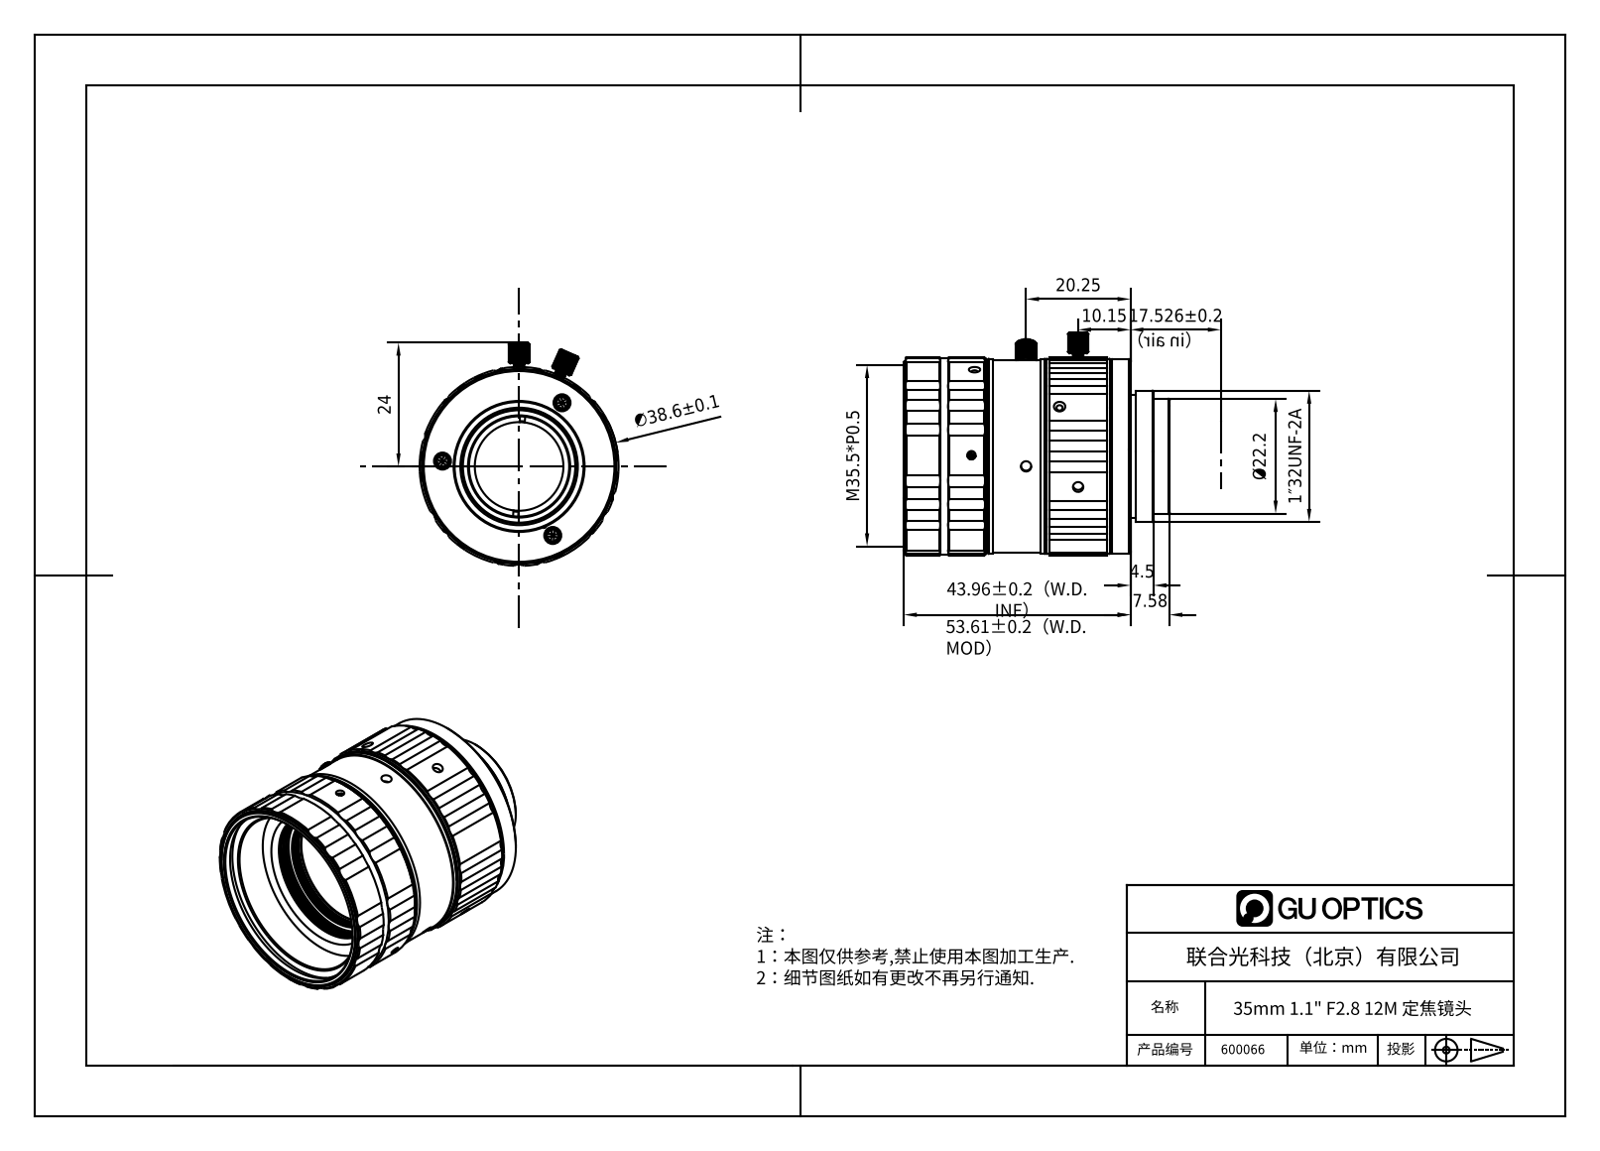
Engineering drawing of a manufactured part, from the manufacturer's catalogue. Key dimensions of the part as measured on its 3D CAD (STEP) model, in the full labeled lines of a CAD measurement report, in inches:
Part name (STEP PRODUCT): 600066
STEP written by: SolidWorks 2020 (CONFIG_CONTROL_DESIGN)
Units: inches
Bodies: 0 solids, 1146 faces (288 planar, 539 cylindrical, 319 other)
Overall size (bounding box): 2.029 × 1.707 × 1.52
Round holes (diameter × count): ⌀0.079 ×5, ⌀0.071 ×3, ⌀0.114 ×3, ⌀0.677 ×1, ⌀0.765 ×1, ⌀0.795 ×1, ⌀0.874 ×1, ⌀0.913 ×1, ⌀0.981 ×1, ⌀1.012 ×1, ⌀1.082 ×1, ⌀1.11 ×1
Round bosses / shafts (diameter × count): ⌀0.063 ×9, ⌀0.098 ×3, ⌀0.049 ×3, ⌀0.047 ×3, ⌀0.079 ×2, ⌀1.52 ×1, ⌀1.496 ×1, ⌀1.488 ×1
Partial cylindrical surfaces — rounded edges, fillets, slot ends (radius × count): R0.079 ×26, R0.118 ×18, R0.044 ×6, R0.133 ×6, R0.135 ×6, R0.044 ×2, R0.506 ×1
Main face-to-face distances: 0.207, 0.091, 1.58, 1.373, 1.451, 0.079, 1.53, 1.347, 1.14, 0.233
Hole centre spacings: 0.587, 1.016, 0.398, 1.016
